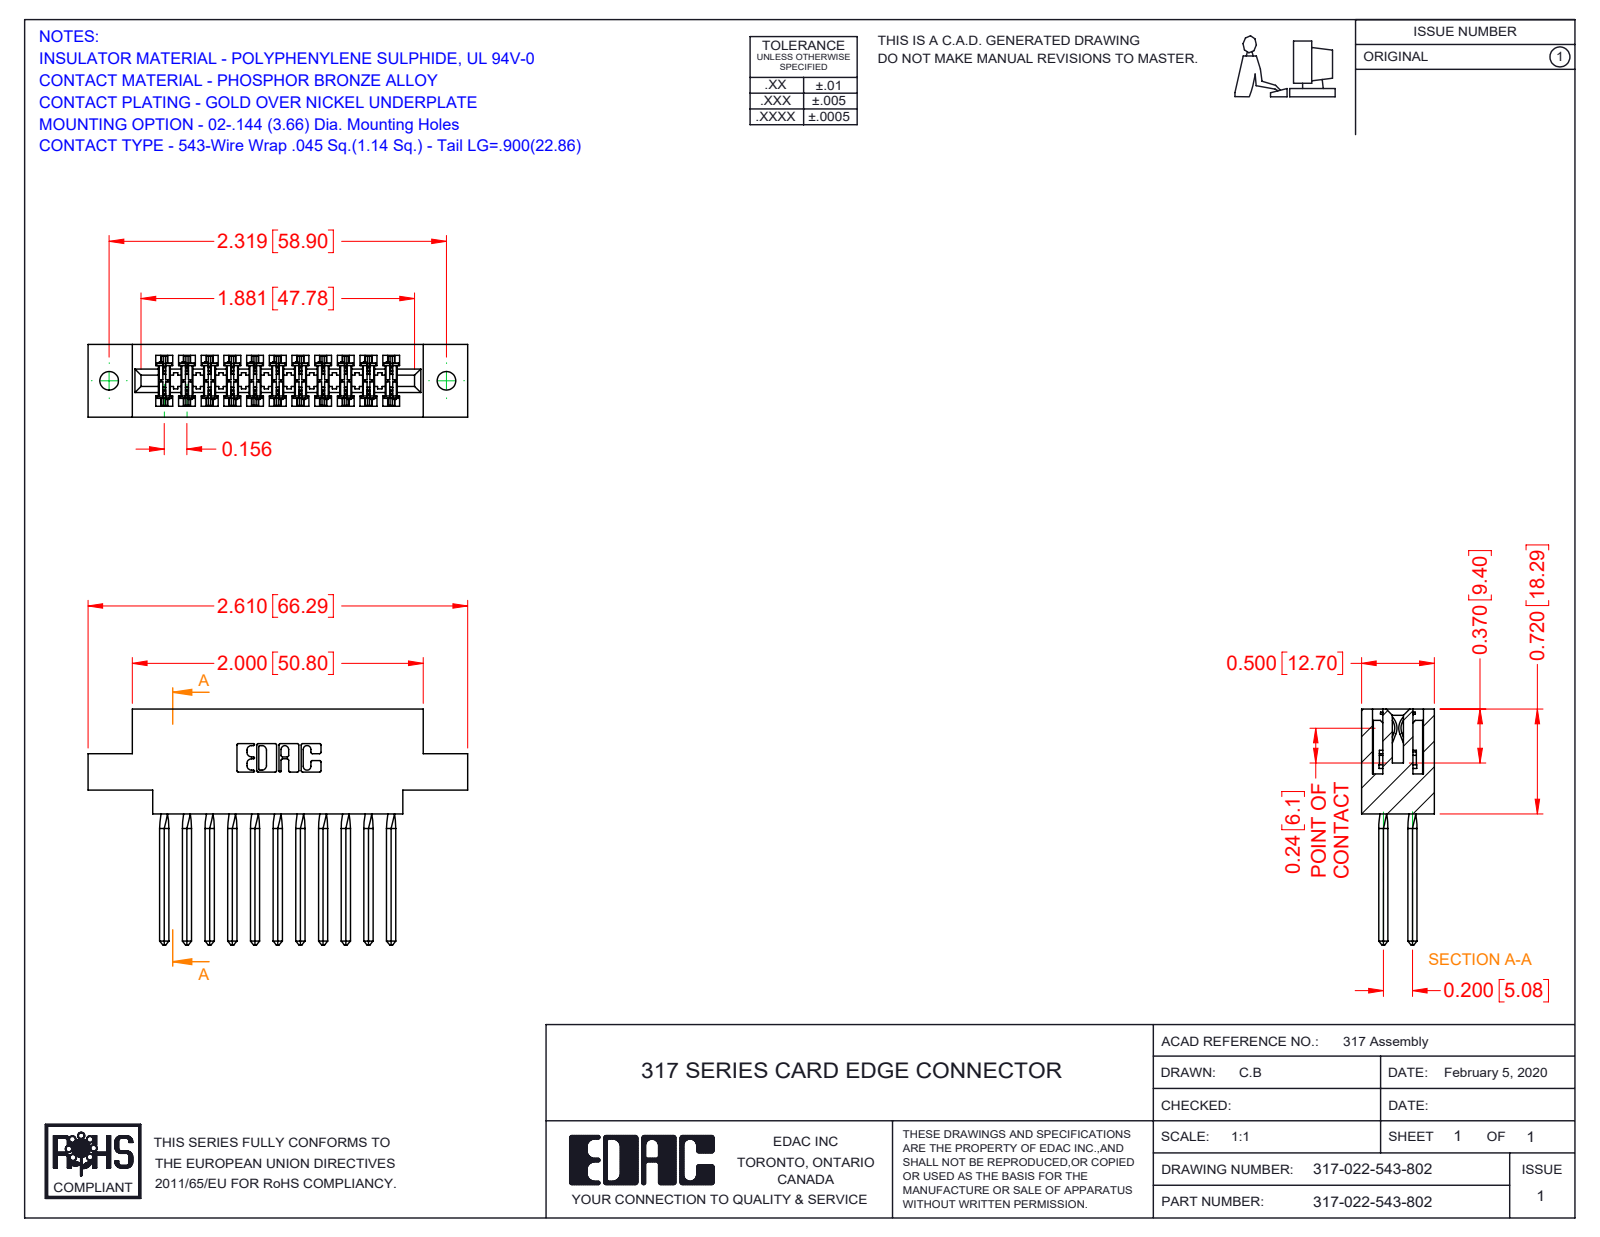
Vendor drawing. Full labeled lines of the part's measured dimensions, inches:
Part name (STEP PRODUCT): 317-290-001_543; 317 Part_.144 Dia; 317-022-543-802
STEP written by: SolidWorks 2016 (CONFIG_CONTROL_DESIGN)
Units: inches
Bodies: 23 solids, 2060 faces (1664 planar, 308 cylindrical, 88 other)
Overall size (bounding box): 2.61 × 1.62 × 0.5
Volume: 0.619 in³ · Surface area: 21.58 in²
Round holes (diameter × count): ⌀0.128 ×2
Partial cylindrical surfaces — rounded edges, fillets, slot ends (radius × count): R0.015 ×44, R0.01 ×22, R0.007 ×6, R0.031 ×6, R0.026 ×3, R0.095 ×2, R0.1 ×2, R0.11 ×2
Main face-to-face distances: 0.5, 0.075, 0.11, 0.425, 0.22, 0.331, 0.35, 0.116, 0.156, 0.552
Hole centre spacings: 2.319
